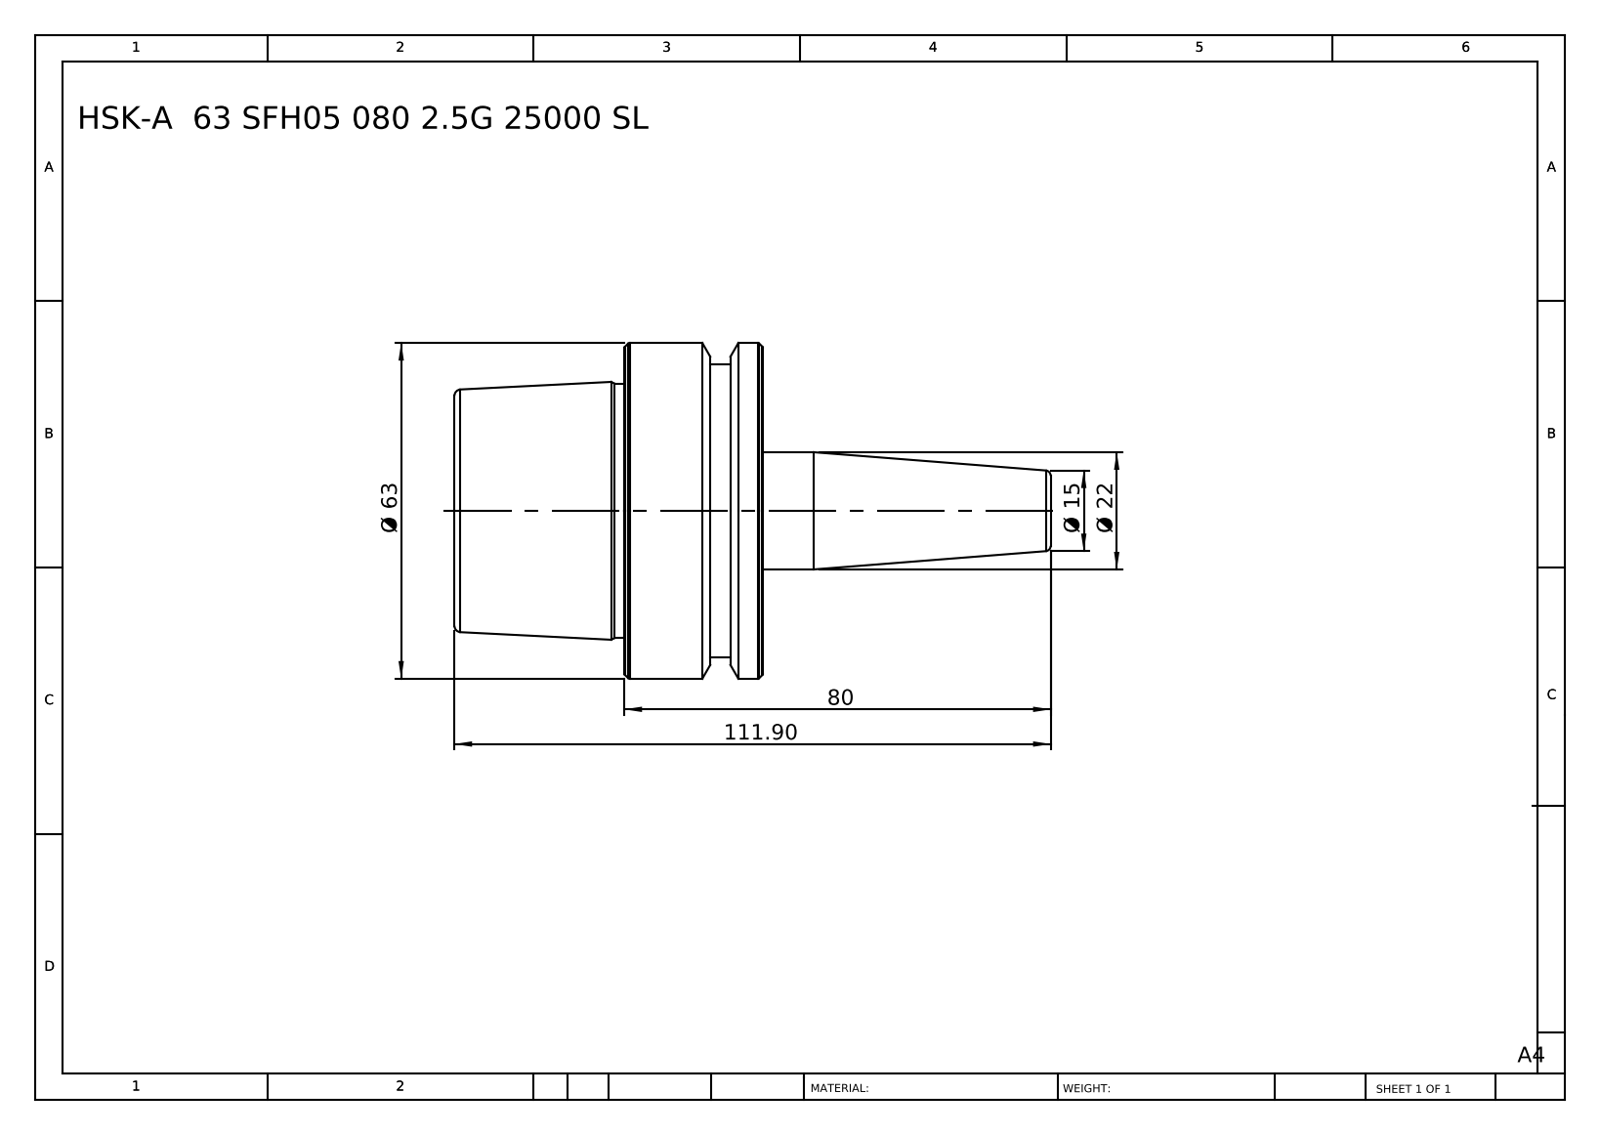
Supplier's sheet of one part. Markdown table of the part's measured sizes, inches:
| quantity | value |
| --- | --- |
| part name | HSK-A 63 SFH04 080 2.5G 25000 SL |
| STEP written by | SolidWorks 2014 (CONFIG_CONTROL_DESIGN) |
| units | inches |
| bodies | 1 solid, 46 faces (6 planar, 10 cylindrical, 30 other) |
| overall size | 4.406 × 2.48 × 2.48 |
| volume | 9.05 in³ |
| surface area | 30.5 in² |
| round bosses / shafts (diameter × count) | 2.48 × 1, 2.165 × 1, 1.881 × 1, 0.866 × 1 |
| main face-to-face distances | 2.28, 1.024, 1.256, 0.24, 0.783, 2.039, 0.39, 0.15, 0.634, 1.89 |
